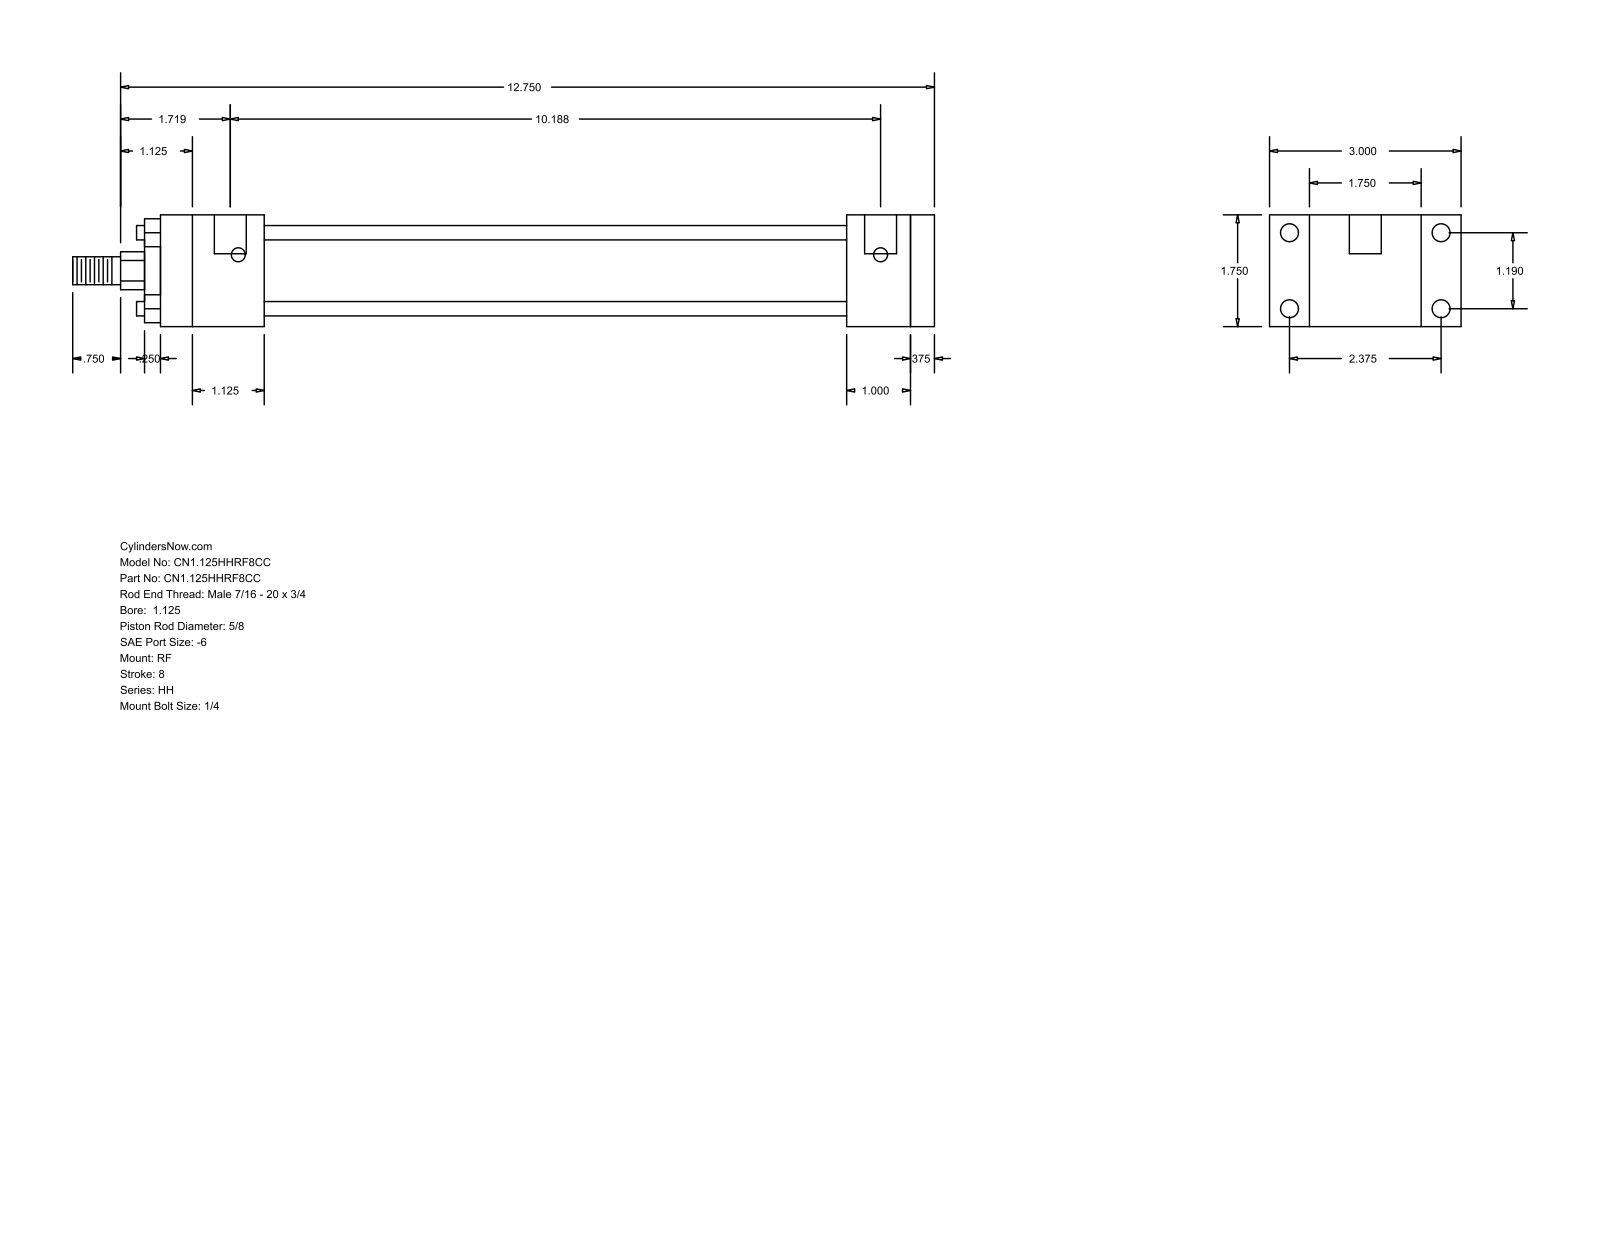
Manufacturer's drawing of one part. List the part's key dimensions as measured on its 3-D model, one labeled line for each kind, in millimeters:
Part name (STEP PRODUCT): HH_RF__0112_0.625
STEP written by: GSSL Pune (CONFIG_CONTROL_DESIGN)
Units: millimetres
Bodies: 0 solids, 92 faces (64 planar, 28 cylindrical, 0 other)
Overall size (bounding box): 342.9 × 76.2 × 44.45
Round holes (diameter × count): ⌀5.56 ×4, ⌀7.14 ×4, ⌀12.7 ×2
Round bosses / shafts (diameter × count): ⌀5.71 ×4, ⌀34.92 ×1, ⌀28.57 ×1, ⌀15.88 ×1, ⌀11.11 ×1
Partial cylindrical surfaces — rounded edges, fillets, slot ends (radius × count): R7.54 ×1
Main face-to-face distances: 44.46, 9.53, 307.97, 15.87, 257.17, 266.7, 231.78, 25.39, 34.92, 41.27
Hole centre spacings: 30.22, 60.32, 67.47, 255.59, 3.17, 258.76
